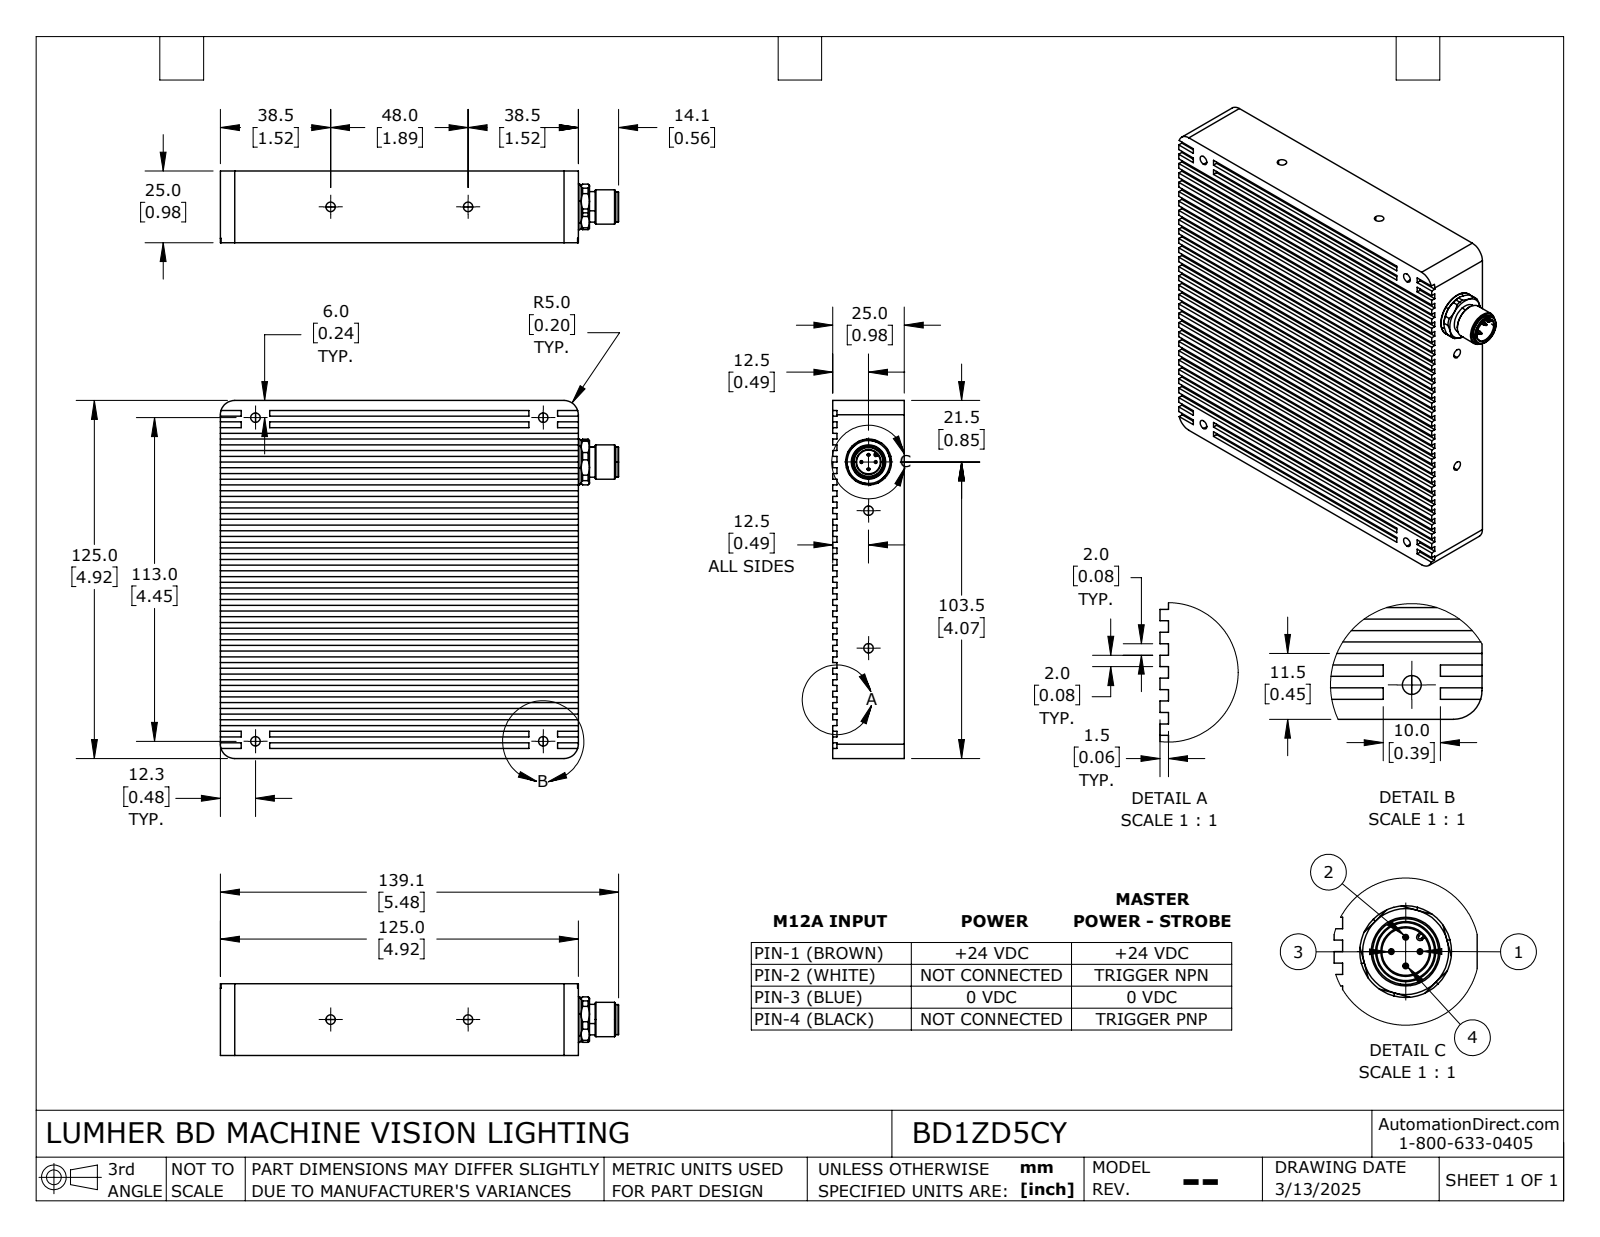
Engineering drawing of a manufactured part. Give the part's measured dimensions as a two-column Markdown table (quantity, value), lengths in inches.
| quantity | value |
| --- | --- |
| part name | BD1__5_Y |
| STEP written by | SolidWorks 2024 (AUTOMOTIVE_DESIGN) |
| units | inches |
| bodies | 1 solid, 1122 faces (229 planar, 561 cylindrical, 332 other) |
| overall size | 5.476 × 4.921 × 0.984 |
| volume | 22.64 in³ |
| surface area | 89.7 in² |
| round holes (diameter × count) | 0.134 × 12, 0.13 × 8, 0.057 × 4, 0.327 × 1, 0.37 × 1 |
| round bosses / shafts (diameter × count) | 0.22 × 12, 0.114 × 12, 0.031 × 12, 0.055 × 4, 0.039 × 4, 0.63 × 1, 0.473 × 1, 0.417 × 1 |
| partial cylindrical surfaces (radius × count) | 0.022 × 144, 0.01 × 72, 0.04 × 12, 0.079 × 4, 0.138 × 4, 0.197 × 4, 0.012 × 2, 0.024 × 1 |
| main face-to-face distances | 0.965, 0.059, 0.906, 4.921, 0.157, 0.315, 0.472, 0.63, 0.787, 4.906 |
| hole center spacings | 5.298, 1.459, 2.918, 3.324, 4.657, 0.098, 0.139, 0.213 |
